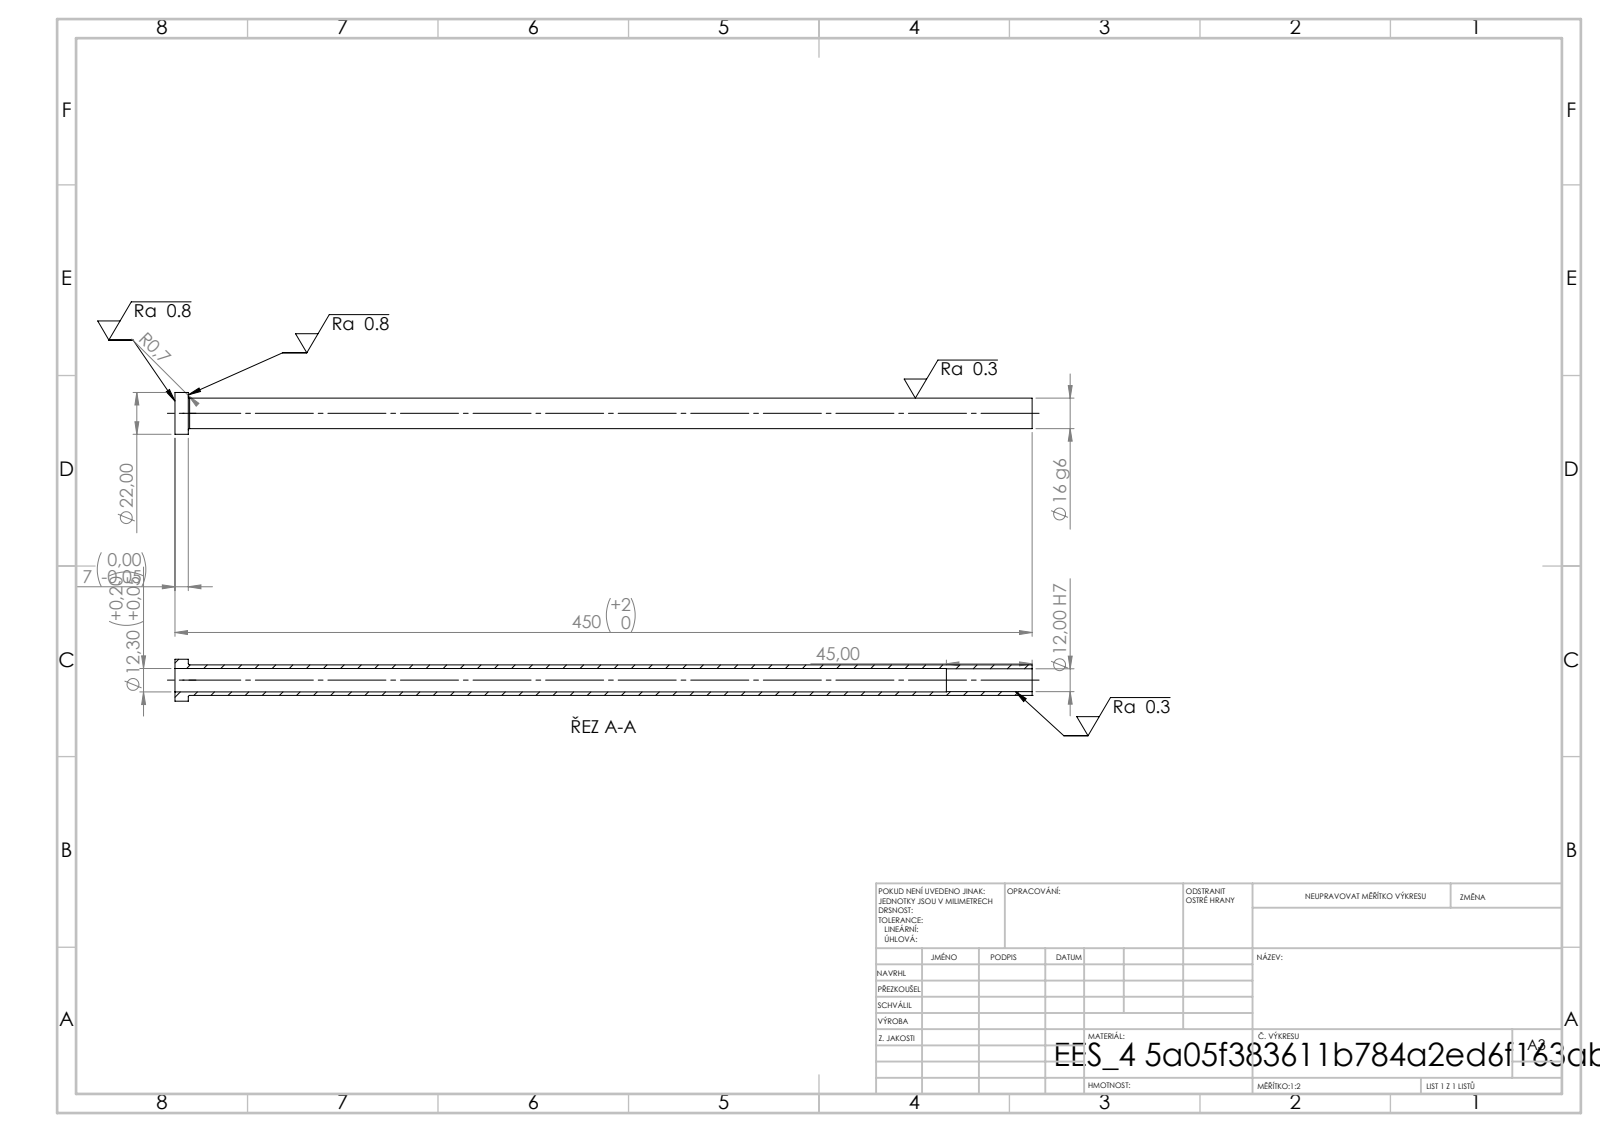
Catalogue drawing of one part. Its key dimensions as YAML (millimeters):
step_written_by: "SolidWorks 2019 (CONFIG_CONTROL_DESIGN)"
units: millimeters
bodies: {solids: 1, faces: 14, planar: 4, cylindrical: 8, other: 2}
overall_size: [450, 22, 22]
volume: 38524
surface_area: 40617
round_holes:
  - {diameter: 12, count: 1}
  - {diameter: 12.3, count: 1}
round_bosses_or_shafts:
  - {diameter: 22, count: 1}
  - {diameter: 16, count: 1}
face_to_face_distances: [7, 450, 443, 405, 398, 45]
